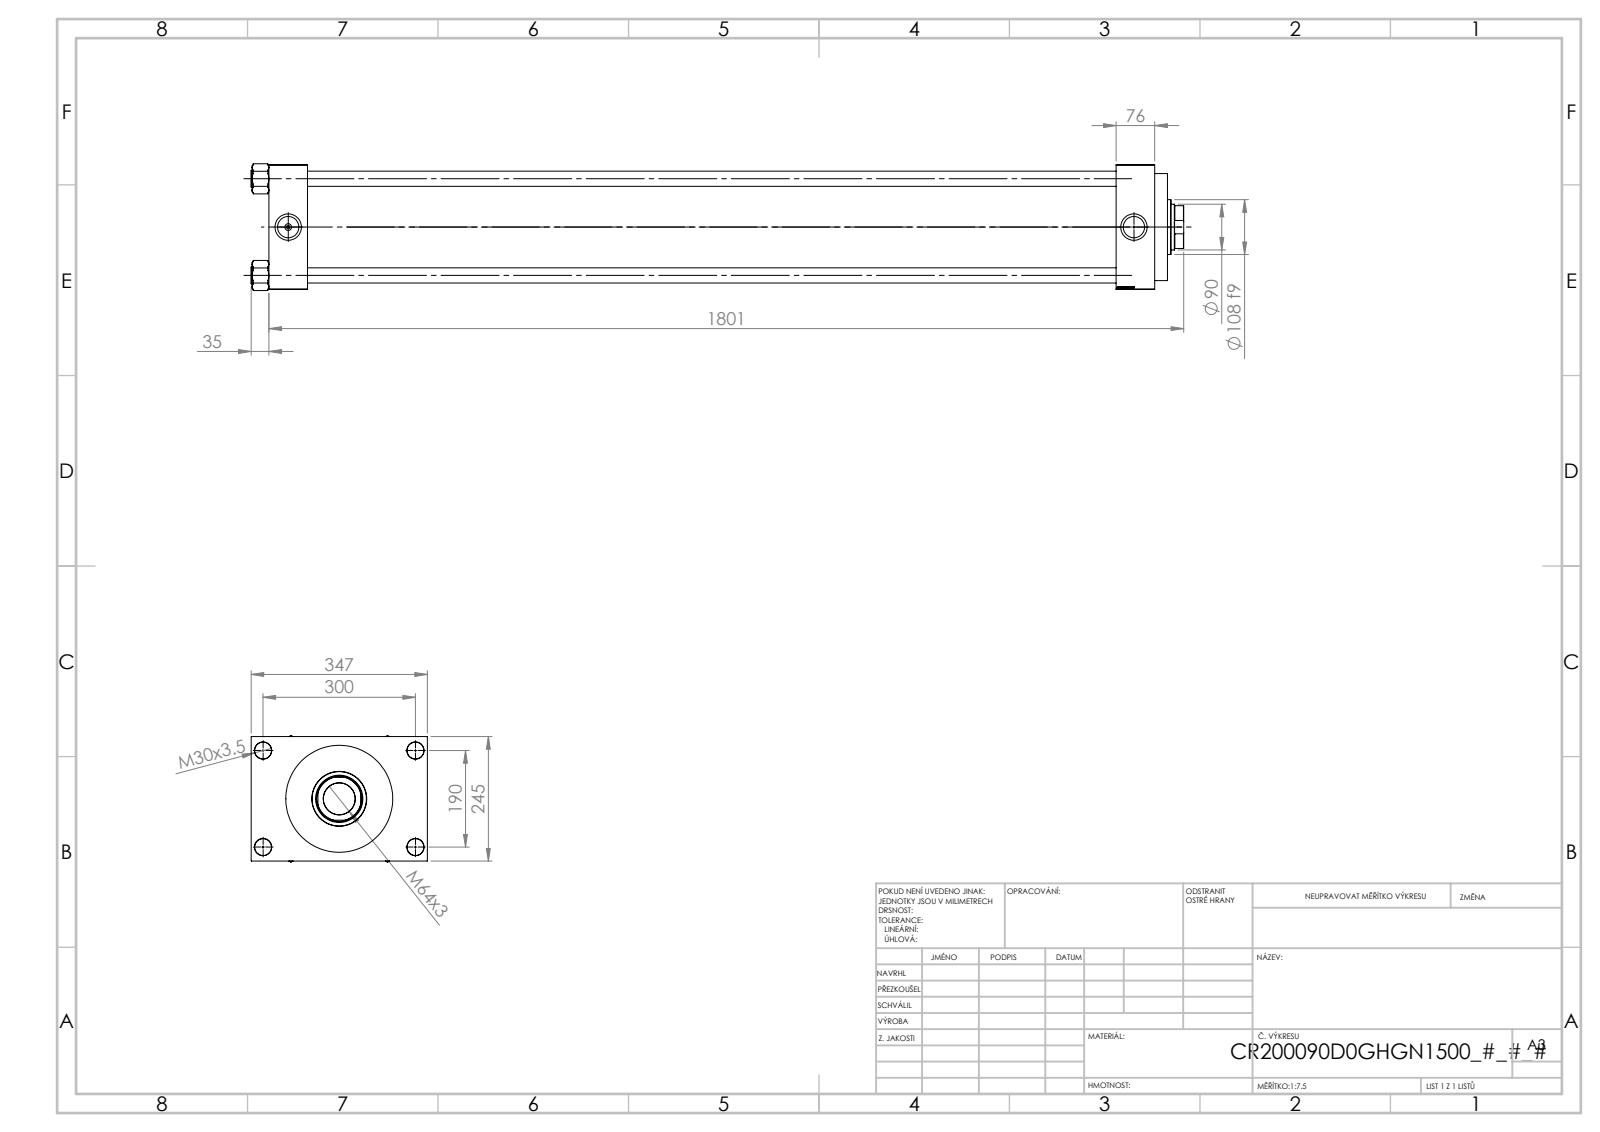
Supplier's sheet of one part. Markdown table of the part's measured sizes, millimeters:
| quantity | value |
| --- | --- |
| part name | V215CR_VCP_D; V215CR_D_Body; V215_VC_A; NUT_M5_D (+1 more) |
| STEP written by | SolidWorks 2019 (CONFIG_CONTROL_DESIGN) |
| units | millimeters |
| bodies | 11 solids, 1148 faces (544 planar, 86 cylindrical, 518 other) |
| overall size | 1836 × 347 × 249.44 |
| volume | 31 080 000 mm³ |
| surface area | 3 961 000 mm² |
| round holes (diameter × count) | 30 × 4, 33 × 4, 7 × 2, 41.92 × 2, 52 × 2, 62.5 × 1, 90 × 1, 93 × 1, 146 × 1, 200 × 1, 210.5 × 1 |
| round bosses / shafts (diameter × count) | 33 × 4, 206 × 1, 108 × 1 |
| partial cylindrical surfaces (radius × count) | 44 × 1 |
| main face-to-face distances | 76, 1668, 245, 1592, 1744, 1725.74, 1649.74, 57.74, 18.26, 51 |
| hole center spacings | 54.9, 134.49, 177.55, 190.2, 197.87, 245.1, 310.18, 190 |
